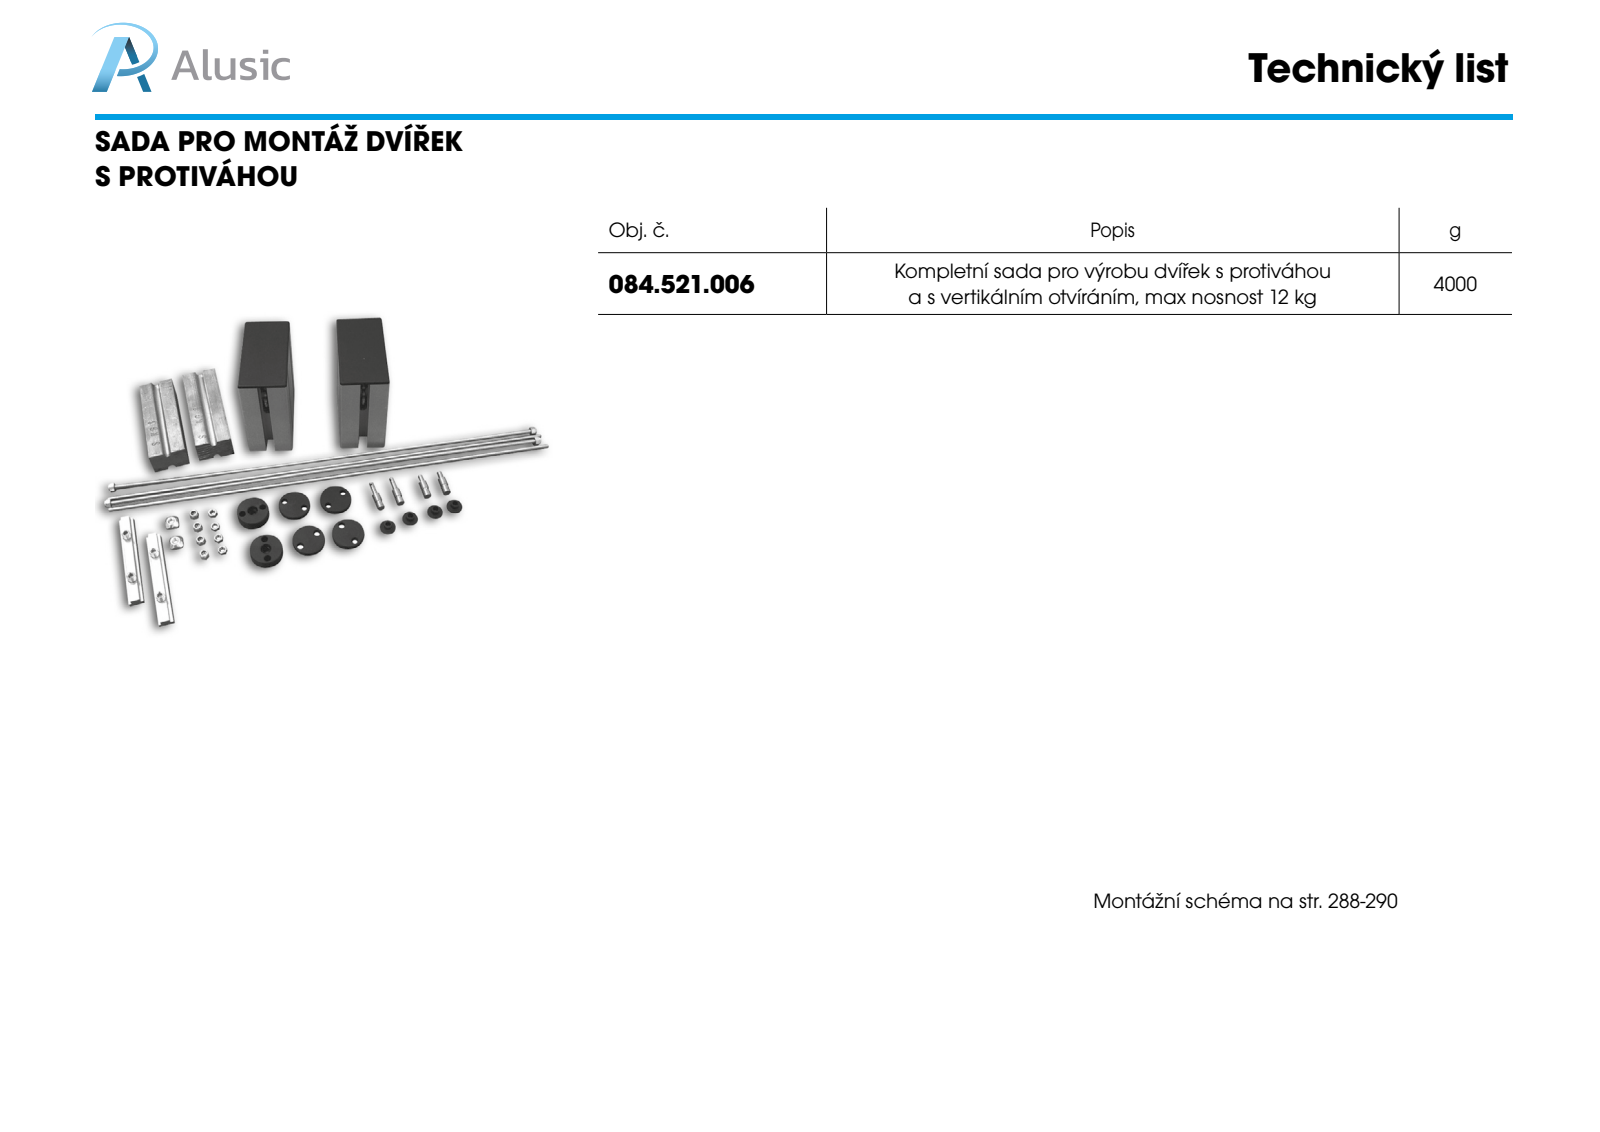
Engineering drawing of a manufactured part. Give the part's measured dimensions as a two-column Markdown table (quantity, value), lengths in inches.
| quantity | value |
| --- | --- |
| part name | 084.521.006; Torque nut 01_ALUSIC_ISO 7040-M5-S; Specchiatura084.521.001 SX; Specchiatura084.202.005 SX (+8 more) |
| STEP written by | SolidWorks 2012 (AUTOMOTIVE_DESIGN) |
| units | inches |
| bodies | 50 solids, 1652 faces (418 planar, 690 cylindrical, 544 other) |
| overall size | 32.784 × 22.835 × 1.815 |
| volume | 28.74 in³ |
| surface area | 412 in² |
| round holes (diameter × count) | 0.268 × 10, 0.394 × 8, 0.217 × 6, 0.165 × 4, 0.197 × 4, 0.231 × 4, 0.079 × 3, 0.201 × 2, 0.311 × 2, 0.315 × 2, 0.354 × 2, 0.472 × 2 |
| round bosses / shafts (diameter × count) | 0.449 × 8, 0.315 × 8, 0.287 × 4, 0.197 × 4, 0.177 × 3, 1.142 × 2, 0.669 × 2, 0.591 × 2 |
| partial cylindrical surfaces (radius × count) | 0.885 × 56, 0.039 × 44, 0.093 × 28, 0.118 × 18, 0.079 × 14, 0.098 × 8, 0.126 × 8, 0.197 × 4 |
| main face-to-face distances | 0.071, 19.291, 1.772, 0.157, 1.224, 1.701, 1.614, 1.154, 1.28, 2.264 |
| hole center spacings | 19.291, 1.772, 0.394, 1.161, 1.201, 1.966, 2.506, 2.929 |
